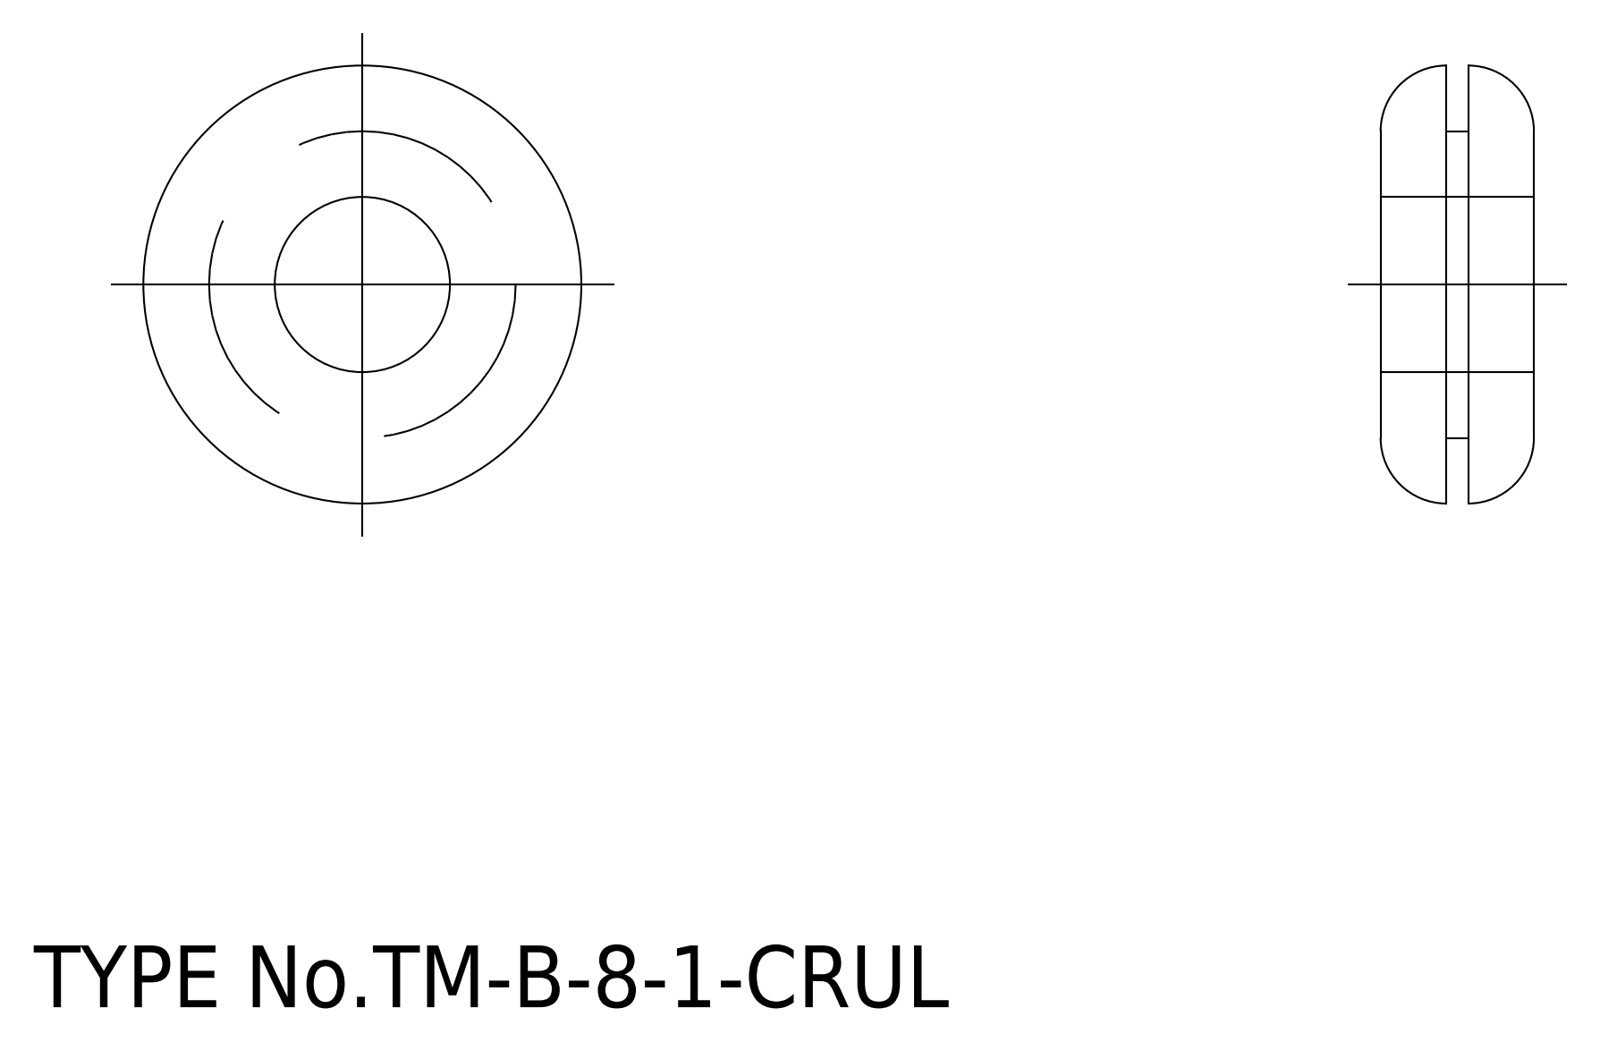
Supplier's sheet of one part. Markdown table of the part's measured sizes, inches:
| quantity | value |
| --- | --- |
| STEP written by | spGate 15.6.1 (AUTOMOTIVE_DESIGN) |
| units | inches |
| bodies | 1 solid, 12 faces (4 planar, 4 cylindrical, 4 other) |
| overall size | 0.787 × 0.787 × 0.276 |
| volume | 0.089 in³ |
| surface area | 1.978 in² |
| round holes (diameter × count) | 0.315 × 1 |
| round bosses / shafts (diameter × count) | 0.551 × 1 |
| main face-to-face distances | 0.118, 0.157, 0.039, 0.276 |
